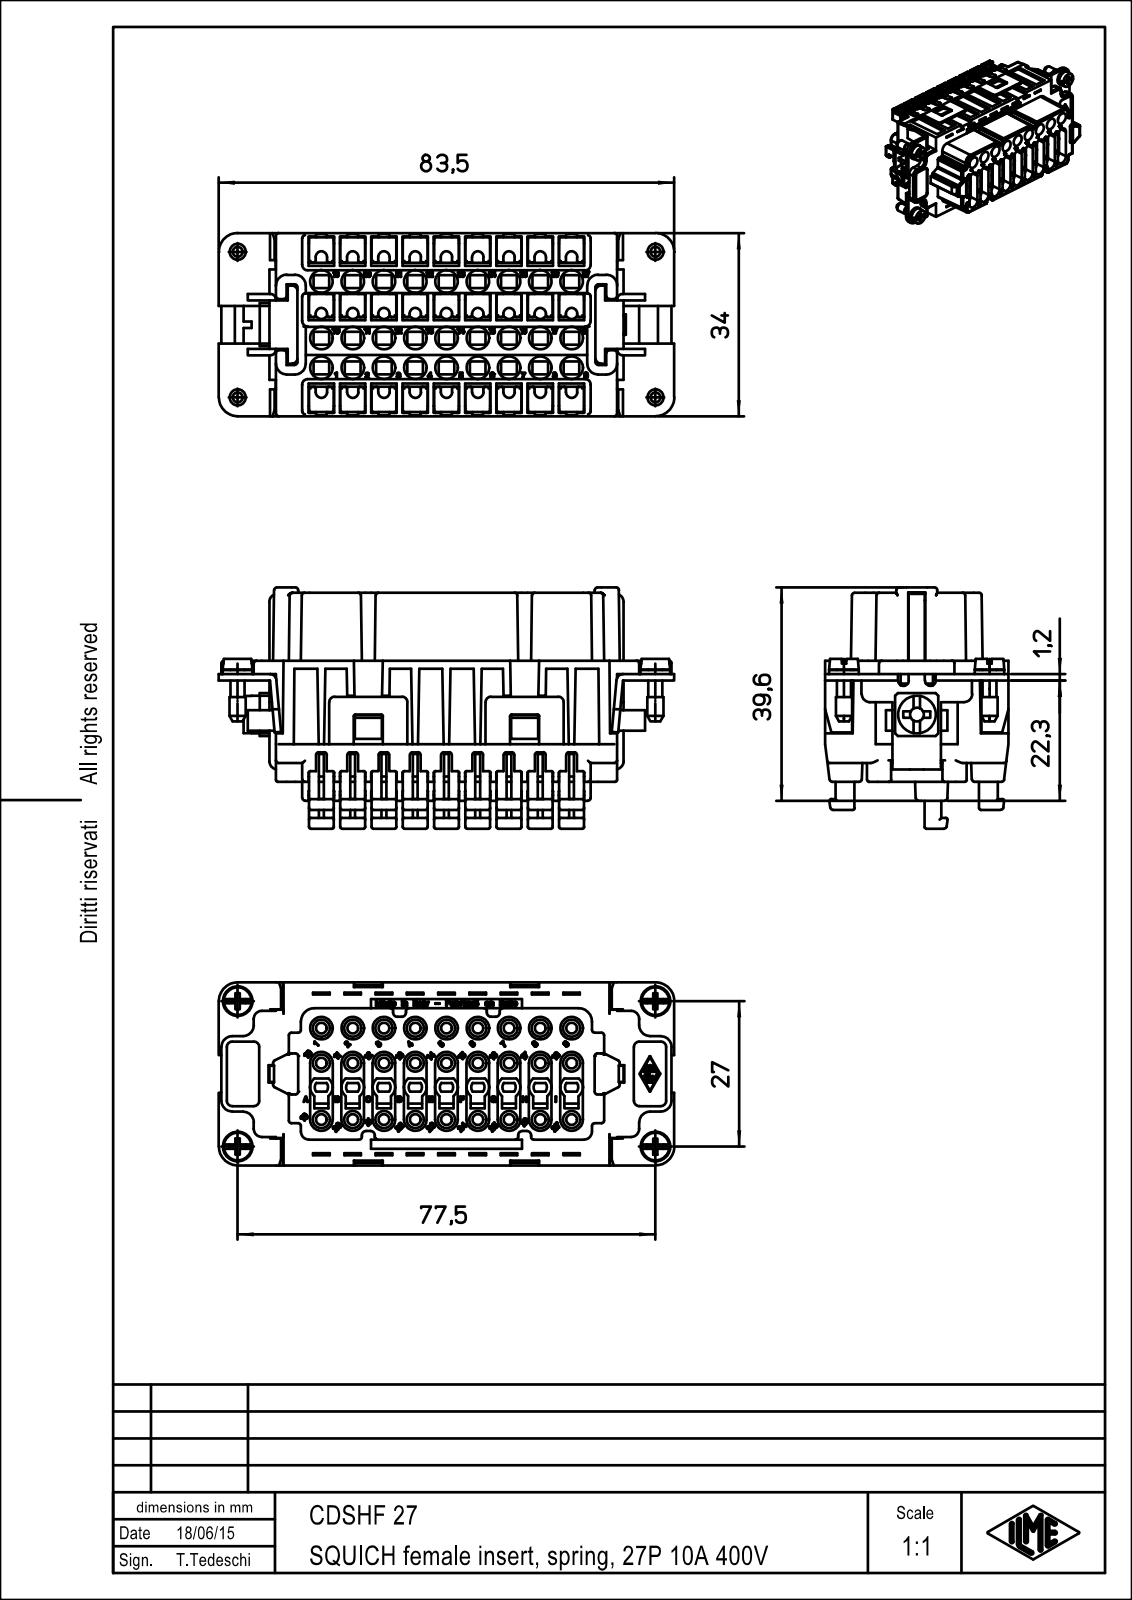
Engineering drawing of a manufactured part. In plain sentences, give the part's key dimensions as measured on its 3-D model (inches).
The part is named "CDSHF_27". Its 3-D file was written by "PTC Creo Elements/Direct Modeling 19.0B 21-Mar-2015 (C) Parametric Technology GmbH (AUTOMOTIVE_DESIGN)". It is 1 solid with 2189 faces: 1691 planar, 360 cylindrical and 138 other. Overall it measures 3.327 by 1.764 by 1.339 inches. Its volume is 3.683 cubic inches and its surface area 47.84 square inches. Round holes: 36 of diameter 0.165, 27 of diameter 0.079, 1 of diameter 0.157. Round bosses or shafts: 4 of diameter 0.217, 4 of diameter 0.118, 1 of diameter 0.276. Partial cylindrical surfaces (rounded edges, fillets, slot ends): 42 of radius 0.02, 27 of radius 0.041, 27 of radius 0.083, 22 of radius 0.039, 16 of radius 0.079, 12 of radius 0.059, 9 of radius 0.043, 9 of radius 0.049. The main face-to-face distances are 0.228, 0.047, 0.457, 0.276, 0.181, 0.685, 0.138, 0.913, 1.142, 0.035. The hole center spacings are 0.228, 0.457, 0.472, 1.142, 1.37, 0.685, 0.616, 0.8.
